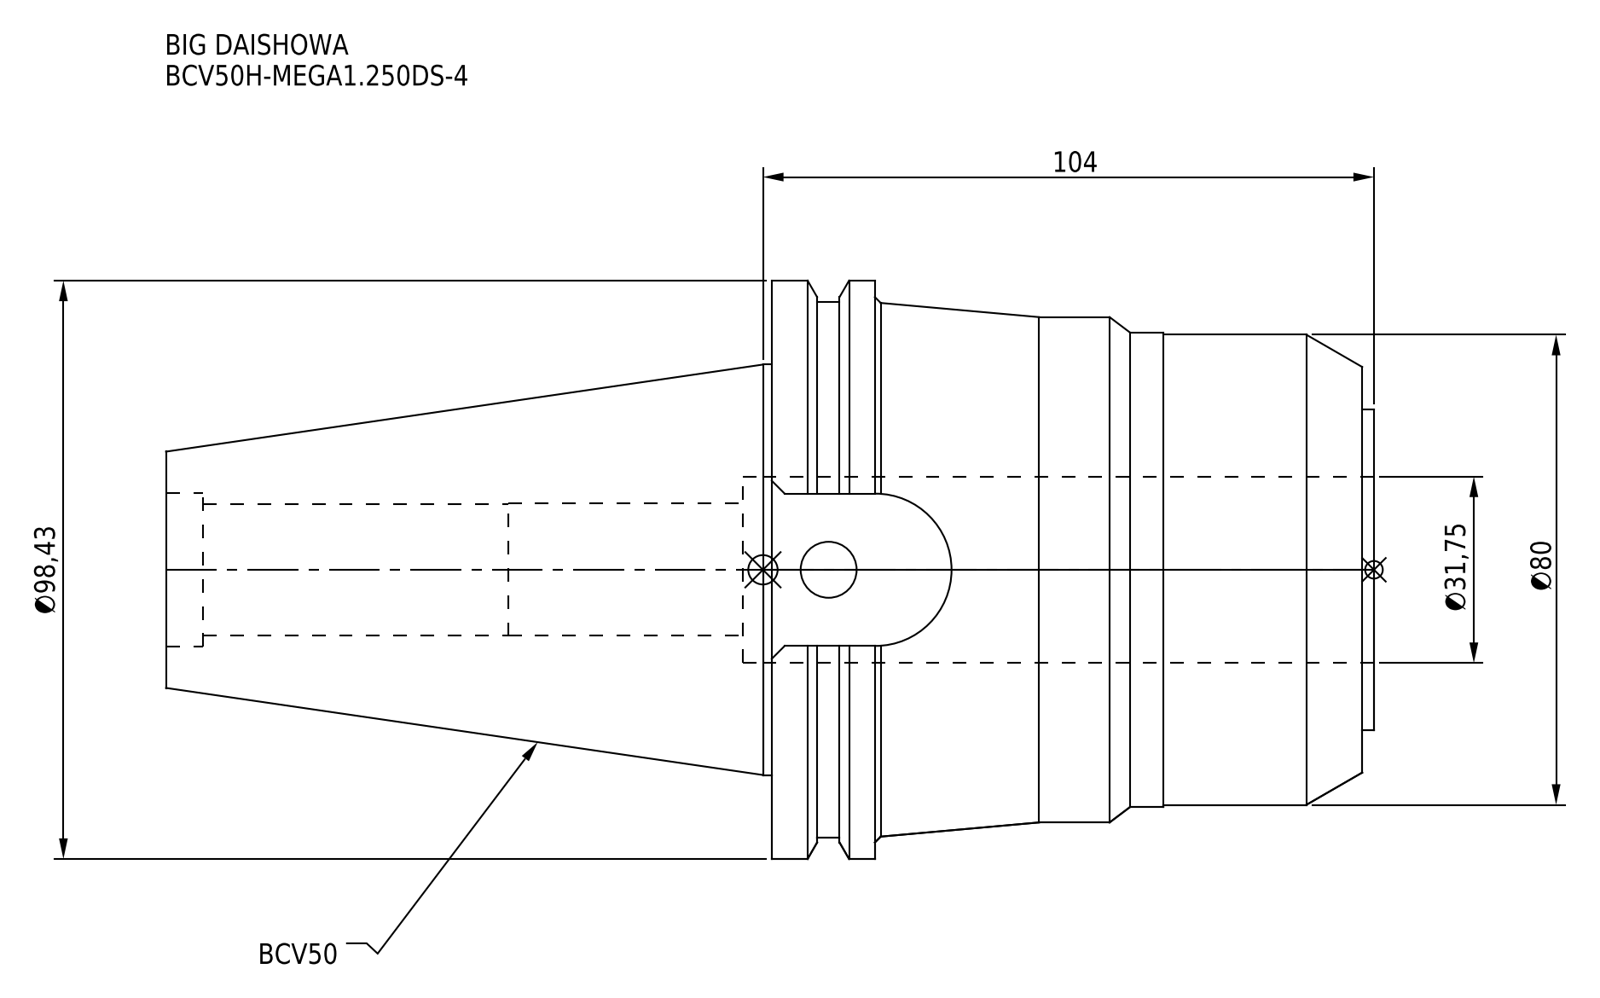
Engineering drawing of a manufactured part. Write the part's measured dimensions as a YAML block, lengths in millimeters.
part_name: "BCV50H-MEGA1_250DS-4"
step_written_by: "CREO PARAMETRIC BY PTC INC, 2016380 (AUTOMOTIVE_DESIGN)"
units: millimeters
bodies: {solids: 1, faces: 69, planar: 25, cylindrical: 30, other: 14}
overall_size: [205.6, 98.42, 94.95]
volume: 700611
surface_area: 74407
round_holes:
  - {diameter: 9.53, count: 1}
  - {diameter: 22.3, count: 1}
  - {diameter: 22.5, count: 1}
  - {diameter: 26.23, count: 1}
  - {diameter: 31.75, count: 1}
round_bosses_or_shafts:
  - {diameter: 98.42, count: 1}
  - {diameter: 91.29, count: 1}
  - {diameter: 86, count: 1}
  - {diameter: 80.7, count: 1}
  - {diameter: 80, count: 1}
  - {diameter: 69.85, count: 1}
  - {diameter: 54.7, count: 1}
partial_cylinders:
  - {radius: 12.96, count: 1}
face_to_face_distances: [102.5, 2, 100.5, 205.6, 203.6, 103.1, 84.95, 82.95, 17.55, 120.65]
